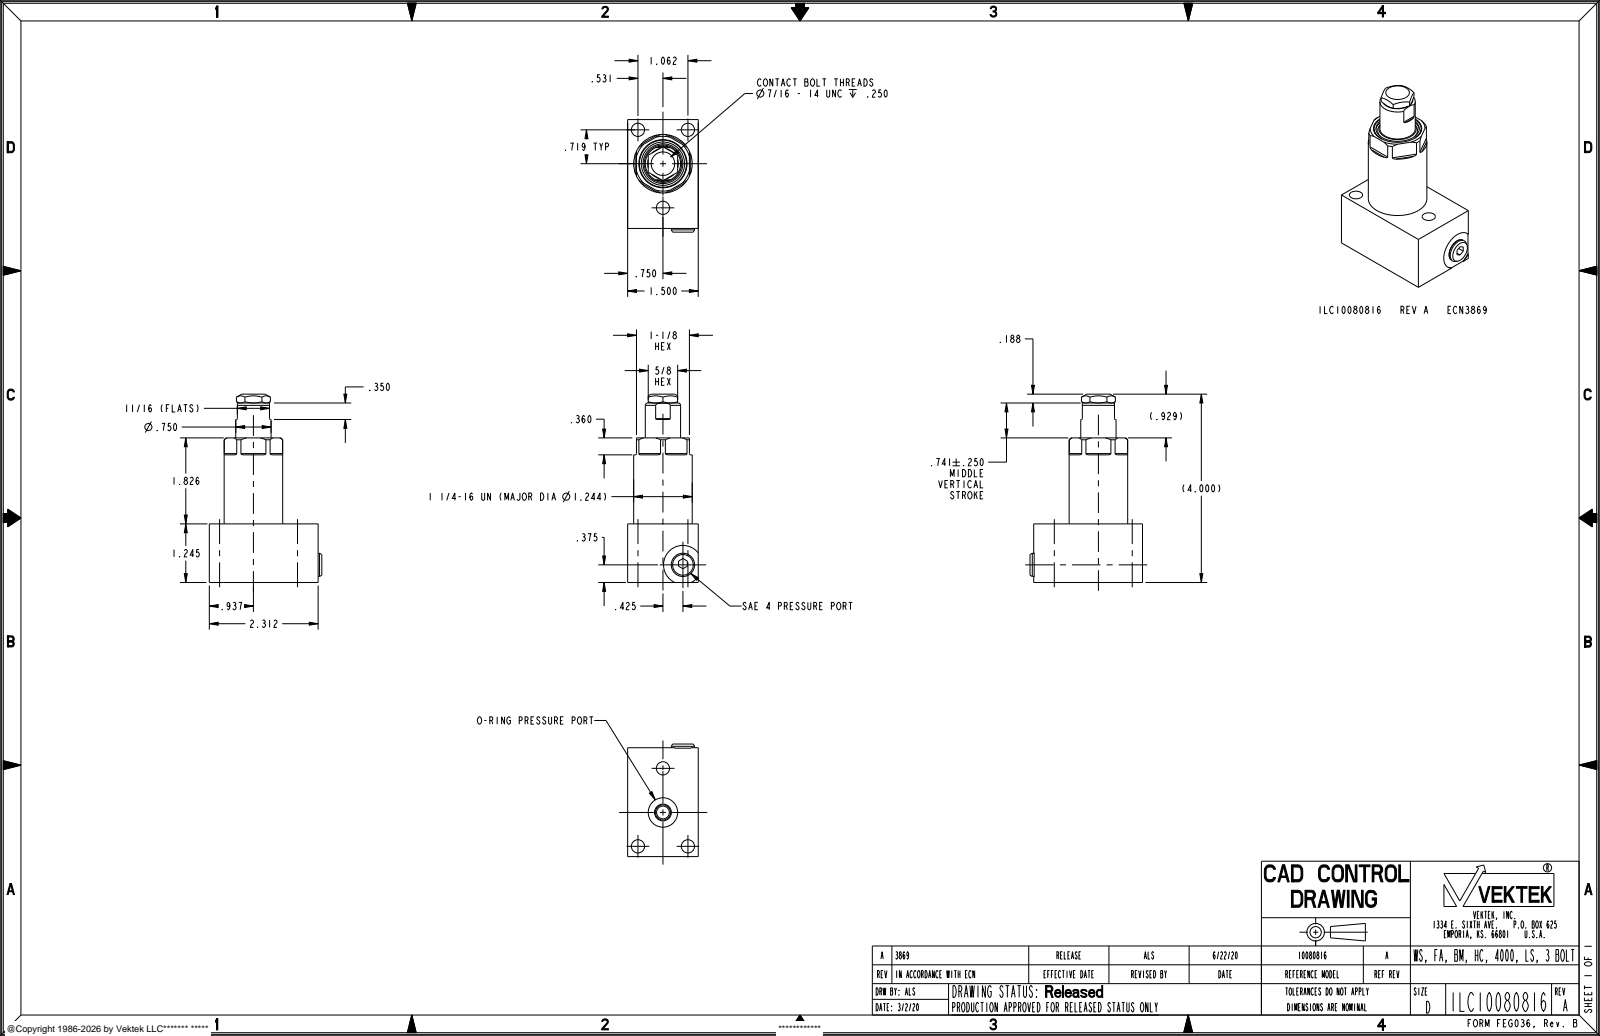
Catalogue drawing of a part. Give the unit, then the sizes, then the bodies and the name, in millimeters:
Units: millimetres
Overall size (bounding box): 101.6 × 60.7 × 38.1
Round holes (diameter × count): ⌀7.1 ×3, ⌀6.9 ×1, ⌀9.3 ×1, ⌀10 ×1, ⌀15.9 ×1, ⌀23.4 ×1
Round bosses / shafts (diameter × count): ⌀11.1 ×2, ⌀31.6 ×1, ⌀25.4 ×1, ⌀19.1 ×1, ⌀11.1 ×1
Partial cylindrical surfaces — rounded edges, fillets, slot ends (radius × count): R0.7 ×6, R0.5 ×2, R10.5 ×1
Main face-to-face distances: 38.1, 31.6, 58.7, 28.6, 6.4, 4.7, 33.4, 58.5, 22.2, 78
Hole centre spacings: 22.7, 44.2, 23.8, 27
Volume: 106 800 mm³ · Surface area: 20 470 mm²
Bodies: 1 solid, 126 faces (50 planar, 38 cylindrical, 38 other)
Part name (STEP PRODUCT): ILC10080816
STEP written by: PRO/ENGINEER BY PARAMETRIC TECHNOLOGY CORPORATION, 2013320 (CONFIG_CONTROL_DESIGN)
